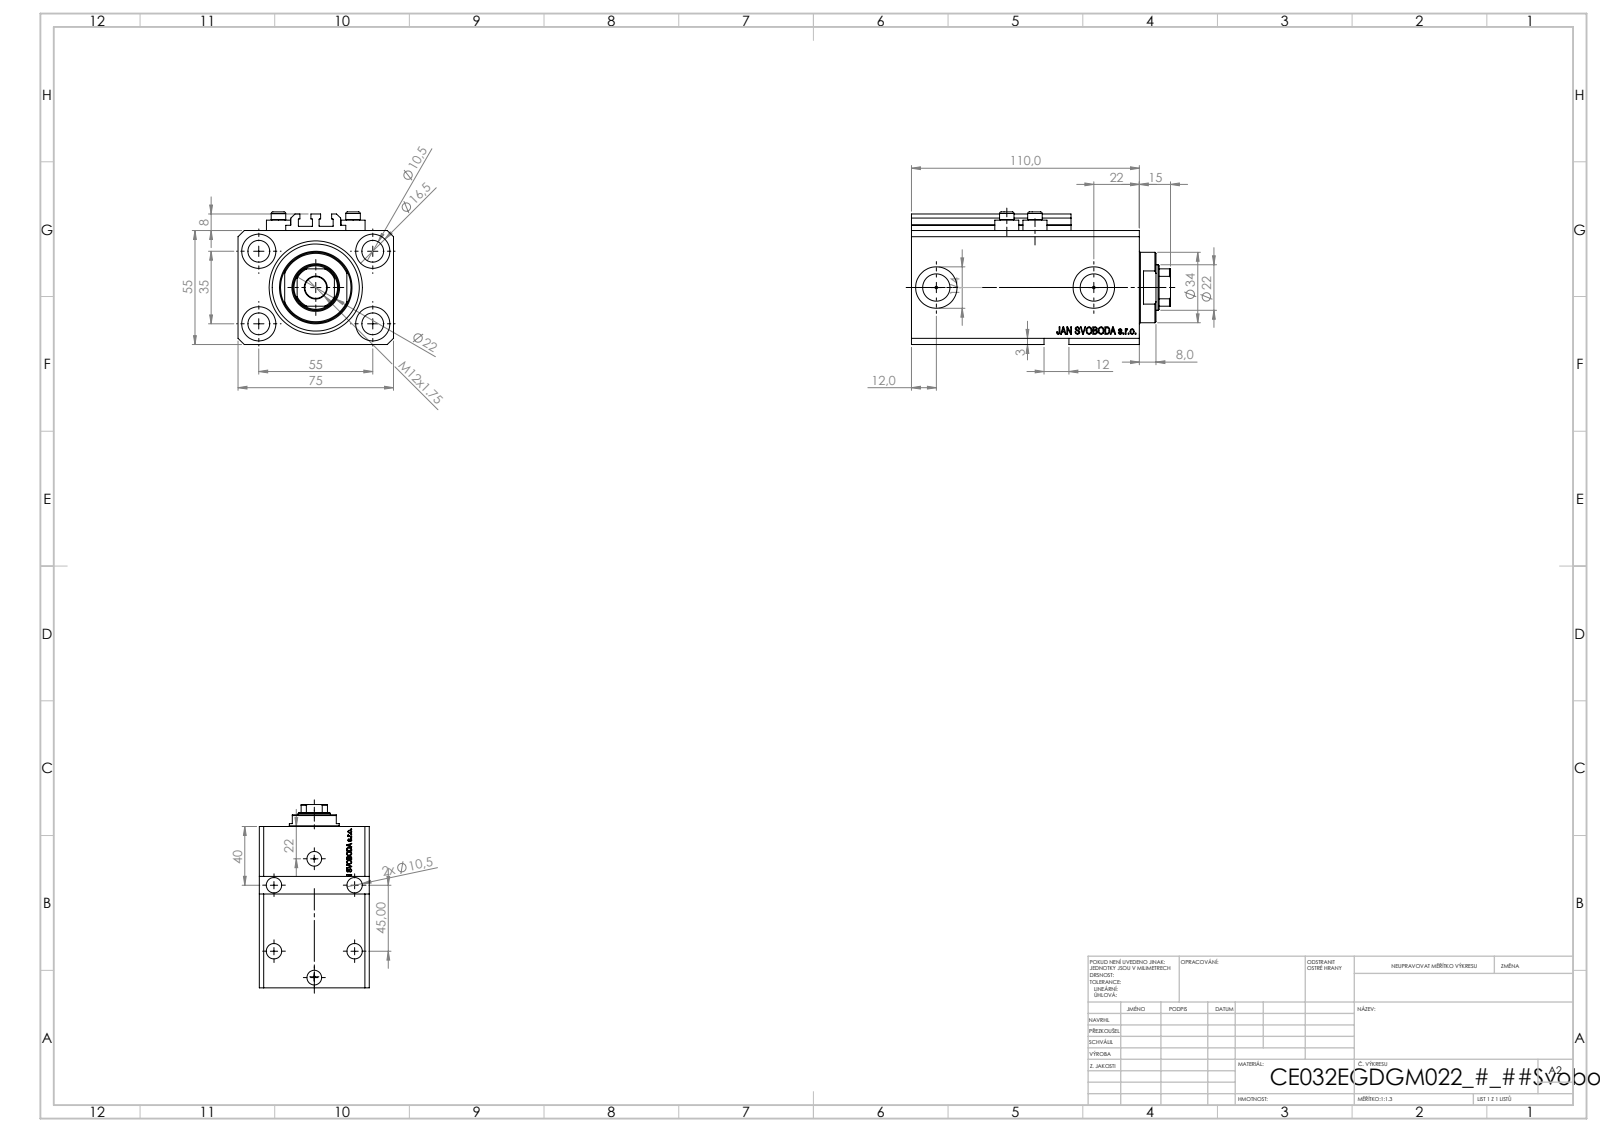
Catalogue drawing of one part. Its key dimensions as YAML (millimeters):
part_name: "ALLEN BOLT V250CE; V250CE_C_VCP; V250CE_E_Body; V250CE_VC_E"
step_written_by: "SolidWorks 2019 (CONFIG_CONTROL_DESIGN)"
units: millimeters
bodies: {solids: 8, faces: 1100, planar: 518, cylindrical: 158, other: 424}
overall_size: [125, 75, 64]
volume: 377718
surface_area: 96791
round_holes:
  - {diameter: 10.5, count: 9}
  - {diameter: 1.25, count: 4}
  - {diameter: 4, count: 4}
  - {diameter: 16.5, count: 4}
  - {diameter: 10, count: 2}
  - {diameter: 13.16, count: 2}
  - {diameter: 20, count: 2}
  - {diameter: 22, count: 1}
  - {diameter: 32, count: 1}
  - {diameter: 45, count: 1}
round_bosses_or_shafts:
  - {diameter: 11.6, count: 4}
  - {diameter: 7, count: 4}
  - {diameter: 34, count: 1}
partial_cylinders:
  - {radius: 0.2, count: 10}
  - {radius: 10.5, count: 1}
face_to_face_distances: [55, 75, 15, 110, 95, 9.9, 3, 85.1, 100.1, 57]
hole_center_spacings: [32.6, 32.87, 55, 68.74, 13.6, 14.09, 23.05, 25.81]
